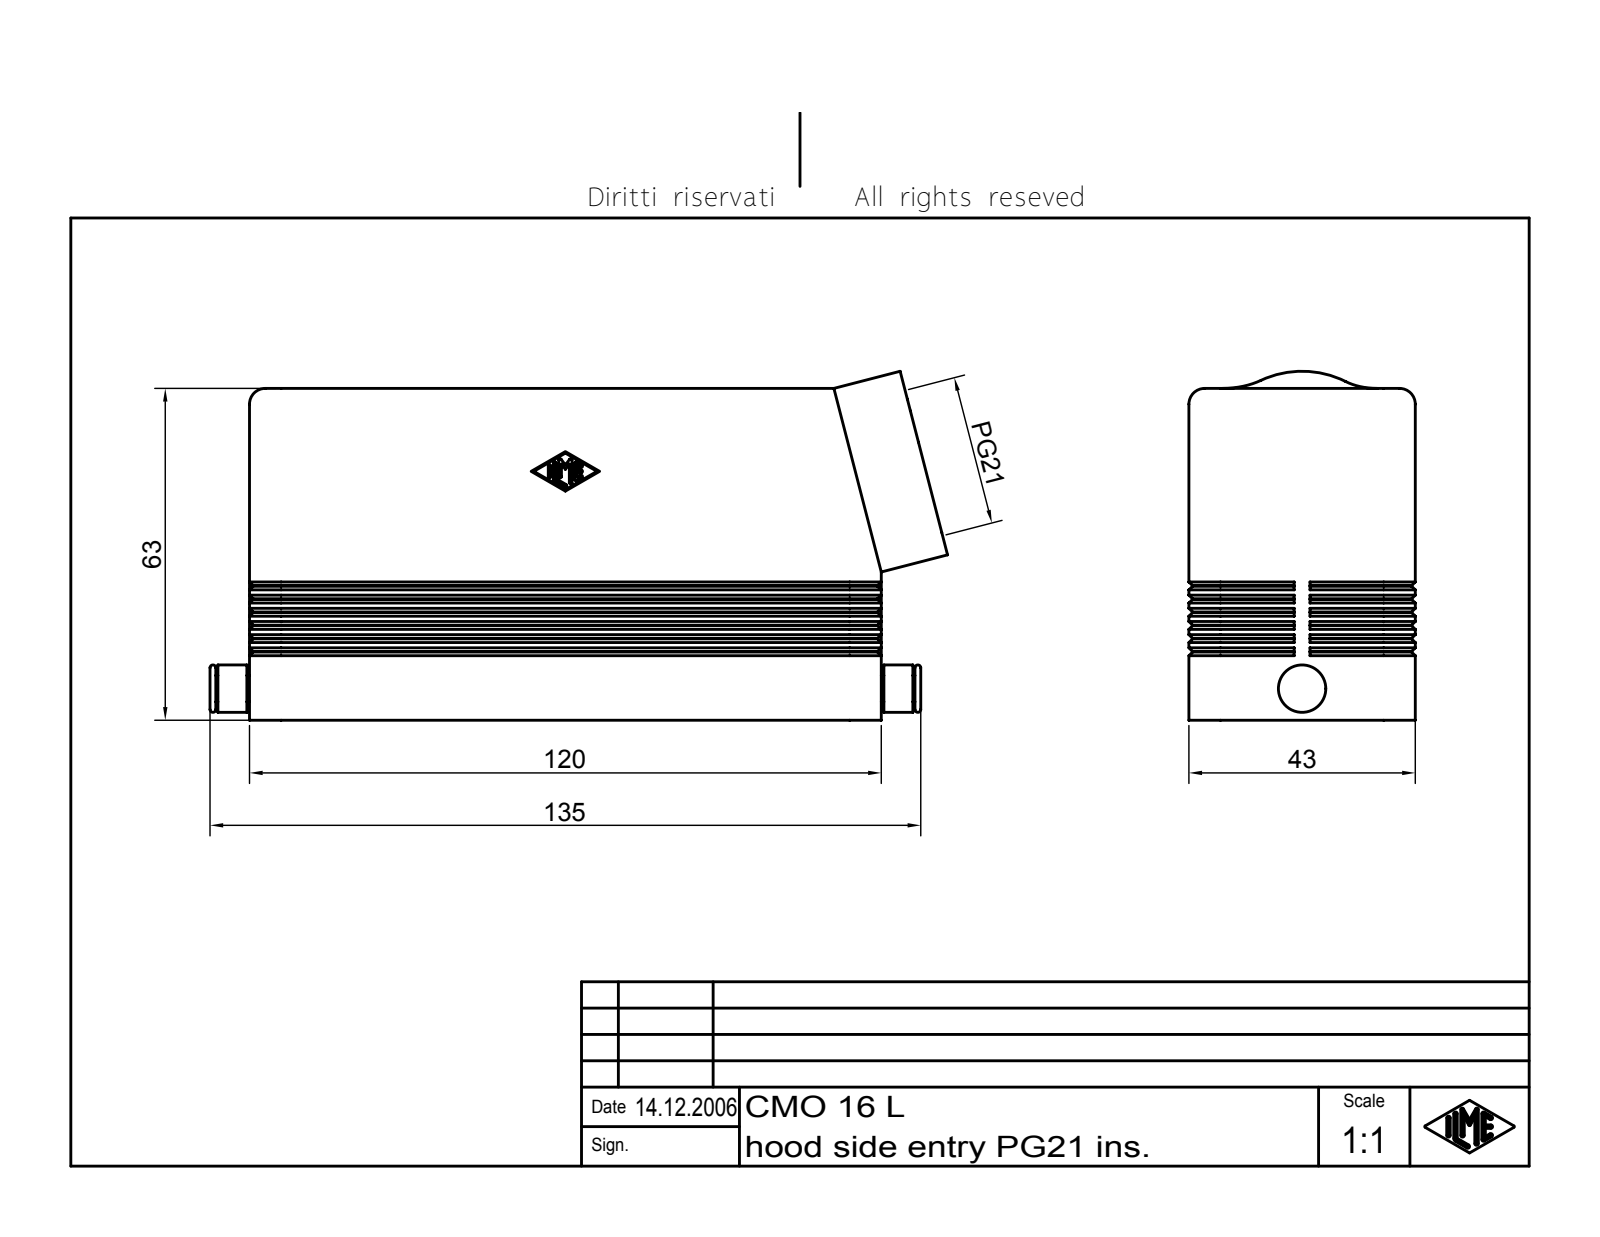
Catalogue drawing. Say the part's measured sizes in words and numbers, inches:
The part is named "CH Tüllengehäuse für einen Einsatz Teil 3". Its 3-D file was written by "Autodesk Inventor 7 (AUTOMOTIVE_DESIGN)". It is 1 solid with 505 faces: 186 planar, 115 cylindrical and 204 other. Overall it measures 5.515 by 2.608 by 1.693 inches. Its volume is 5.382 cubic inches and its surface area 79.12 square inches. Round holes: 1 of diameter 0.976, 1 of diameter 1.054. Round bosses or shafts: 1 of diameter 0.354, 1 of diameter 0.197. Partial cylindrical surfaces (rounded edges, fillets, slot ends): 14 of radius 0.01, 7 of radius 0.118, 4 of radius 0.079, 4 of radius 0.236, 2 of radius 0.209, 1 of radius 0.059. The main face-to-face distances are 0.118, 1.575, 1.457, 1.693, 0.335, 0.453, 0.07, 0.209, 4.154, 1.155.
